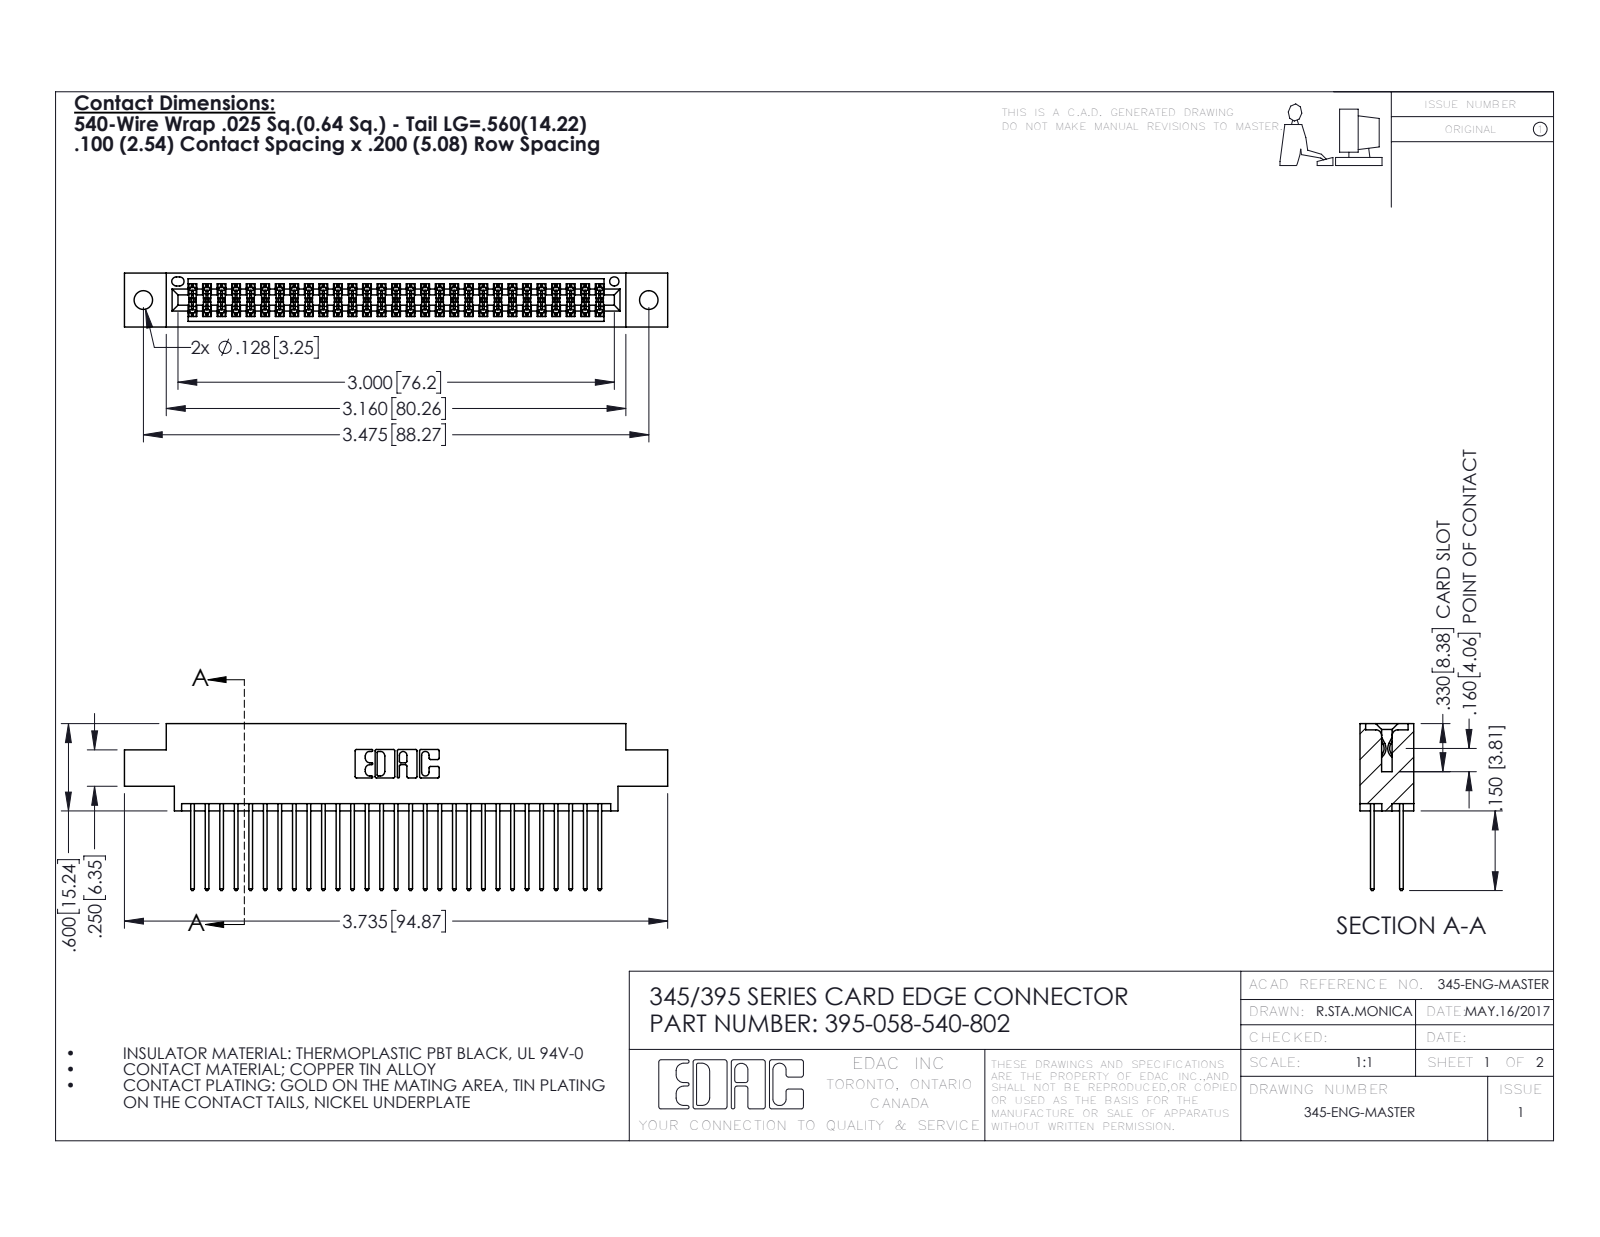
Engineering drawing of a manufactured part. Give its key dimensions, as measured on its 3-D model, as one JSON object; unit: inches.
{"part_name": "395-058-540-802; 345 Part_0.170 Offset - 0.128 Dia; 345-292-001_345-293-140", "step_written_by": "SolidWorks 2016 (CONFIG_CONTROL_DESIGN)", "units": "inches", "bodies": {"solids": 59, "faces": 3030, "planar": 1998, "cylindrical": 1032, "other": 0}, "overall_size": [3.735, 1.147, 0.37], "volume_in3": 0.559, "surface_area_in2": 21.99, "round_holes": [[0.128, 2], [0.064, 1]], "partial_cylinders_radius": [[0.006, 87], [0.01, 58], [0.01, 22], [0.007, 6], [0.031, 6], [0.026, 3], [0.014, 2], [0.019, 2]], "face_to_face_distances": [0.298, 0.072, 0.2, 0.098, 0.272, 0.025, 0.37, 0.225, 0.175, 0.149], "hole_center_spacings": [0.27, 3.24, 3.475]}
